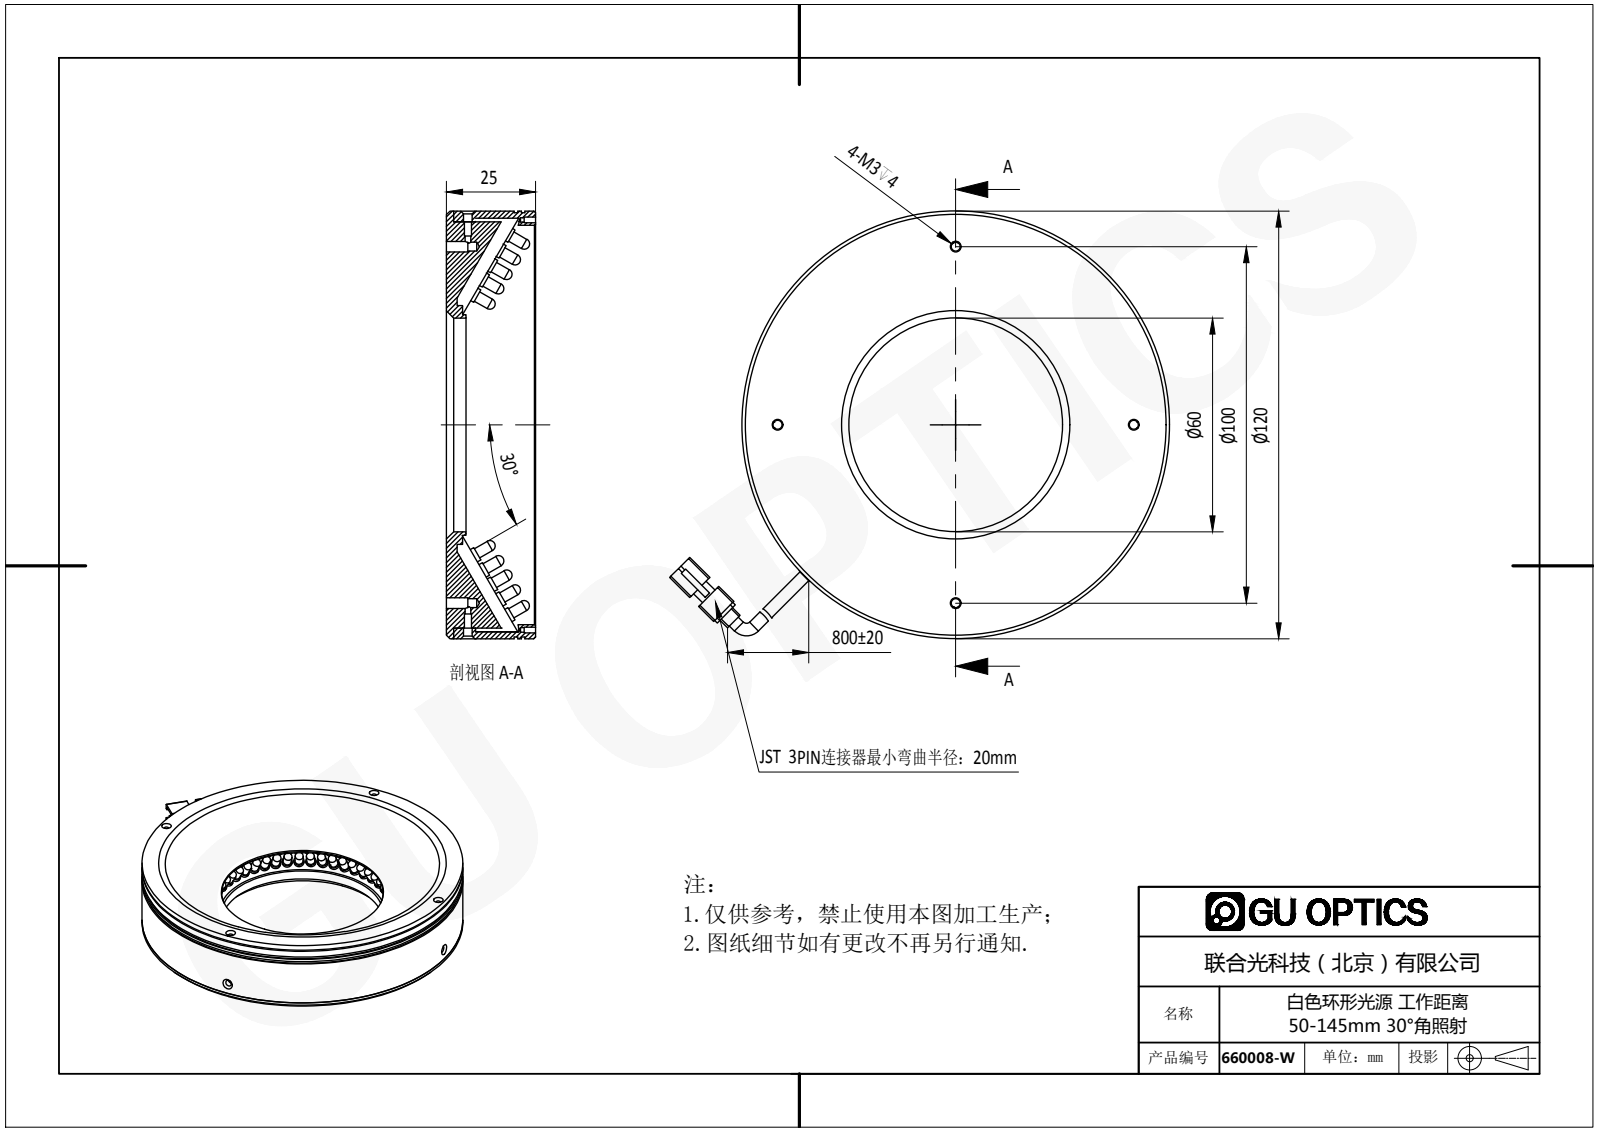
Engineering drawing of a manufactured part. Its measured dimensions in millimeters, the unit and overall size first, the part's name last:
Units: millimetres
Overall size (bounding box): 140.26 × 120 × 29.45
Round holes (diameter × count): ⌀1.6 ×6, ⌀3.5 ×5, ⌀1.25 ×4, ⌀1.7 ×4, ⌀2.5 ×4, ⌀3 ×4, ⌀2 ×2, ⌀2.4 ×2, ⌀60 ×1, ⌀112 ×1, ⌀116 ×1
Round bosses / shafts (diameter × count): ⌀3.8 ×315, ⌀3 ×315, ⌀3.5 ×2, ⌀120 ×1, ⌀119 ×1, ⌀114 ×1, ⌀67 ×1, ⌀61.86 ×1
Partial cylindrical surfaces — rounded edges, fillets, slot ends (radius × count): R0.5 ×12, R1 ×4, R1.65 ×1, R8 ×1
Main face-to-face distances: 25, 2, 1, 23, 27, 0.5, 3, 2.5, 3.5, 20.15
Hole centre spacings: 76.2, 7.5, 50, 57.5, 70.71, 81.32, 107.5, 5.2
Volume: 123 170 mm³ · Surface area: 110 533 mm²
Bodies: 321 solids, 5663 faces (3870 planar, 1401 cylindrical, 392 other)
Part name (STEP PRODUCT): 660008-W
STEP written by: SolidWorks 2016 (AUTOMOTIVE_DESIGN)
